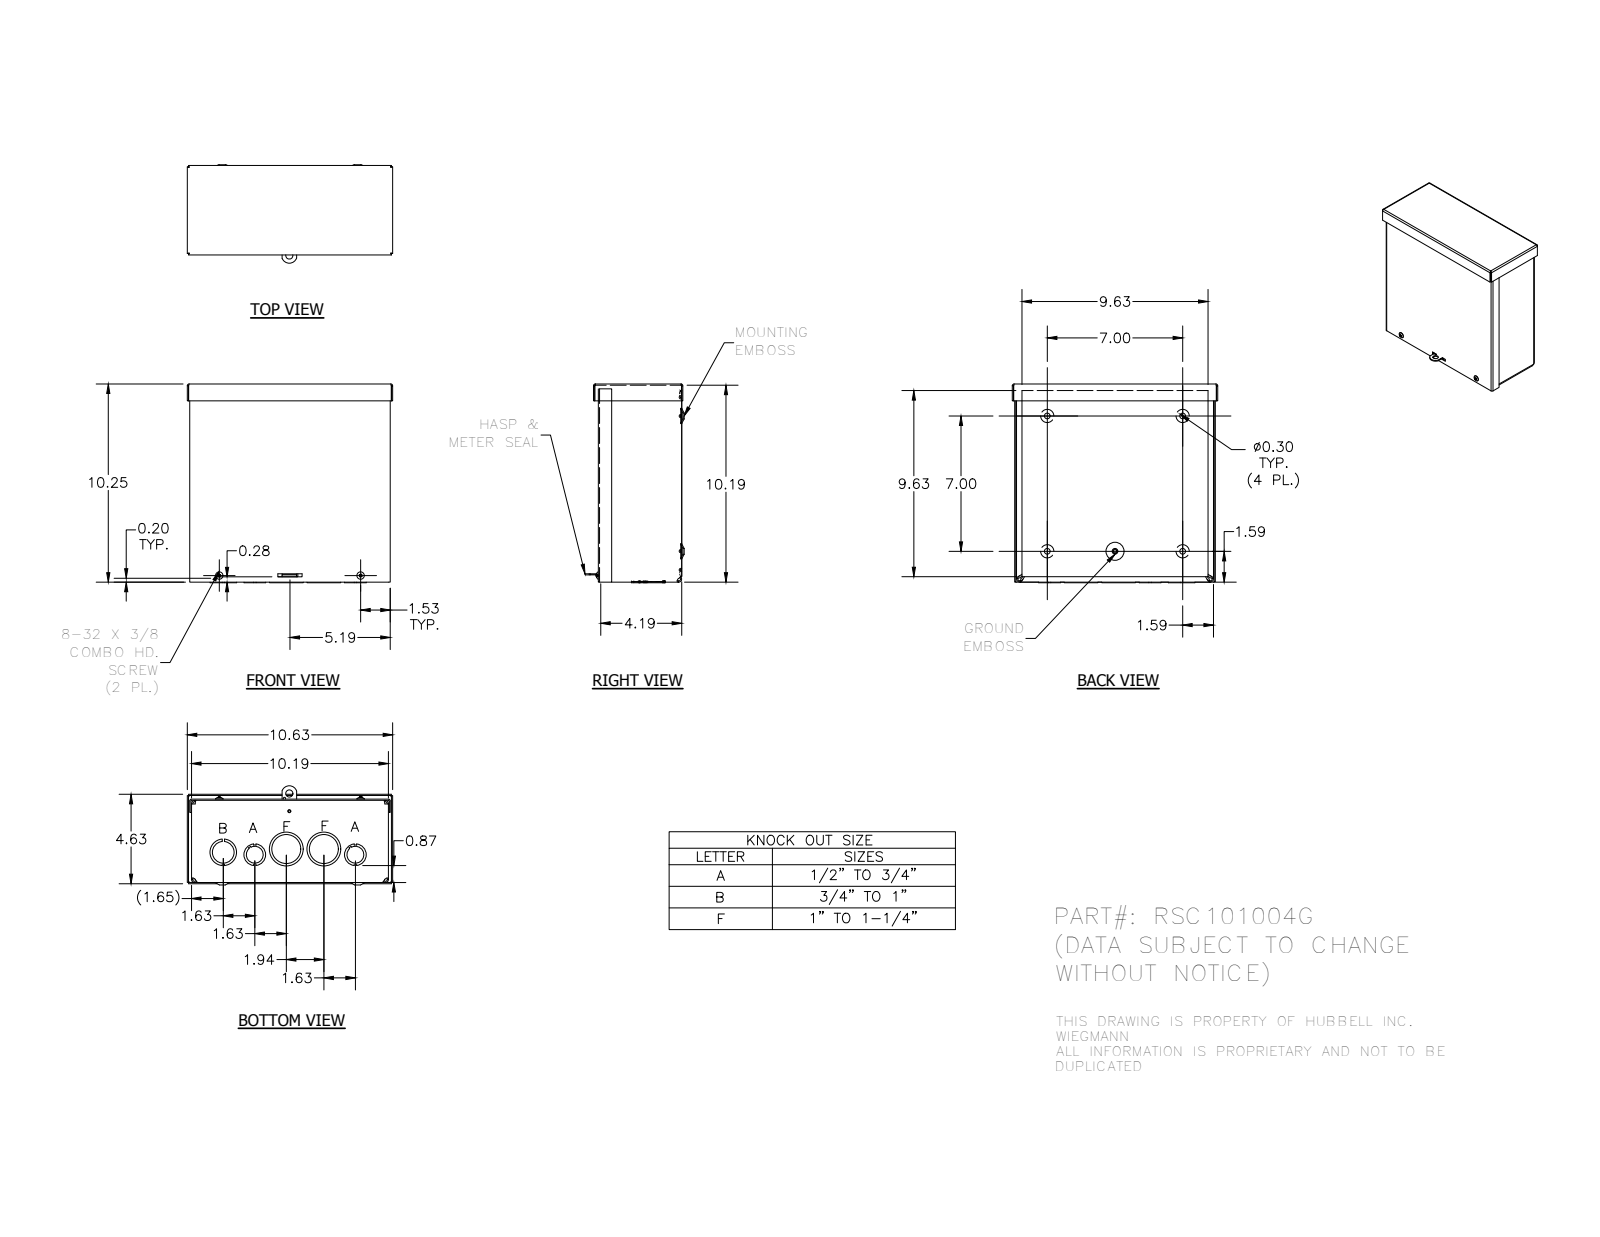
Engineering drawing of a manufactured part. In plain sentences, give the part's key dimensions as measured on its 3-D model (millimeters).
The part is named "RSC101004G_WRAP; RSC1010G_LID; RSC1004G_CAP; 3183 (+4 more)". Its 3-D file was written by "Autodesk Inventor 2014 (AUTOMOTIVE_DESIGN)". It is 7 solids with 518 faces: 245 planar, 129 cylindrical and 144 other. Overall it measures 269.88 by 261.12 by 130.17 millimeters. Its volume is 514 383 cubic millimeters and its surface area 663 907 square millimeters. Round holes: 4 of diameter 7.62, 4 of diameter 7.95, 3 of diameter 28.57, 2 of diameter 3.17, 2 of diameter 3.76, 2 of diameter 22.22, 2 of diameter 38.1, 2 of diameter 44.45, 1 of diameter 3.96, 1 of diameter 4.19, 1 of diameter 9.52, 1 of diameter 34.92. Round bosses or shafts: 2 of diameter 9.75, 2 of diameter 4.17, 1 of diameter 5.8. Partial cylindrical surfaces (rounded edges, fillets, slot ends): 10 of radius 0.25, 8 of radius 0.79, 8 of radius 2.37, 8 of radius 3.17, 8 of radius 4.75, 4 of radius 0.79, 4 of radius 1.4, 4 of radius 1.57. The main face-to-face distances are 1.58, 257.19, 1.57, 107.93, 106.35, 1.59, 109.52, 107.94, 258.77, 3.15. The hole center spacings are 177.8, 27.24, 32.03, 42.07, 88.9, 90.99, 185.75, 198.78.
